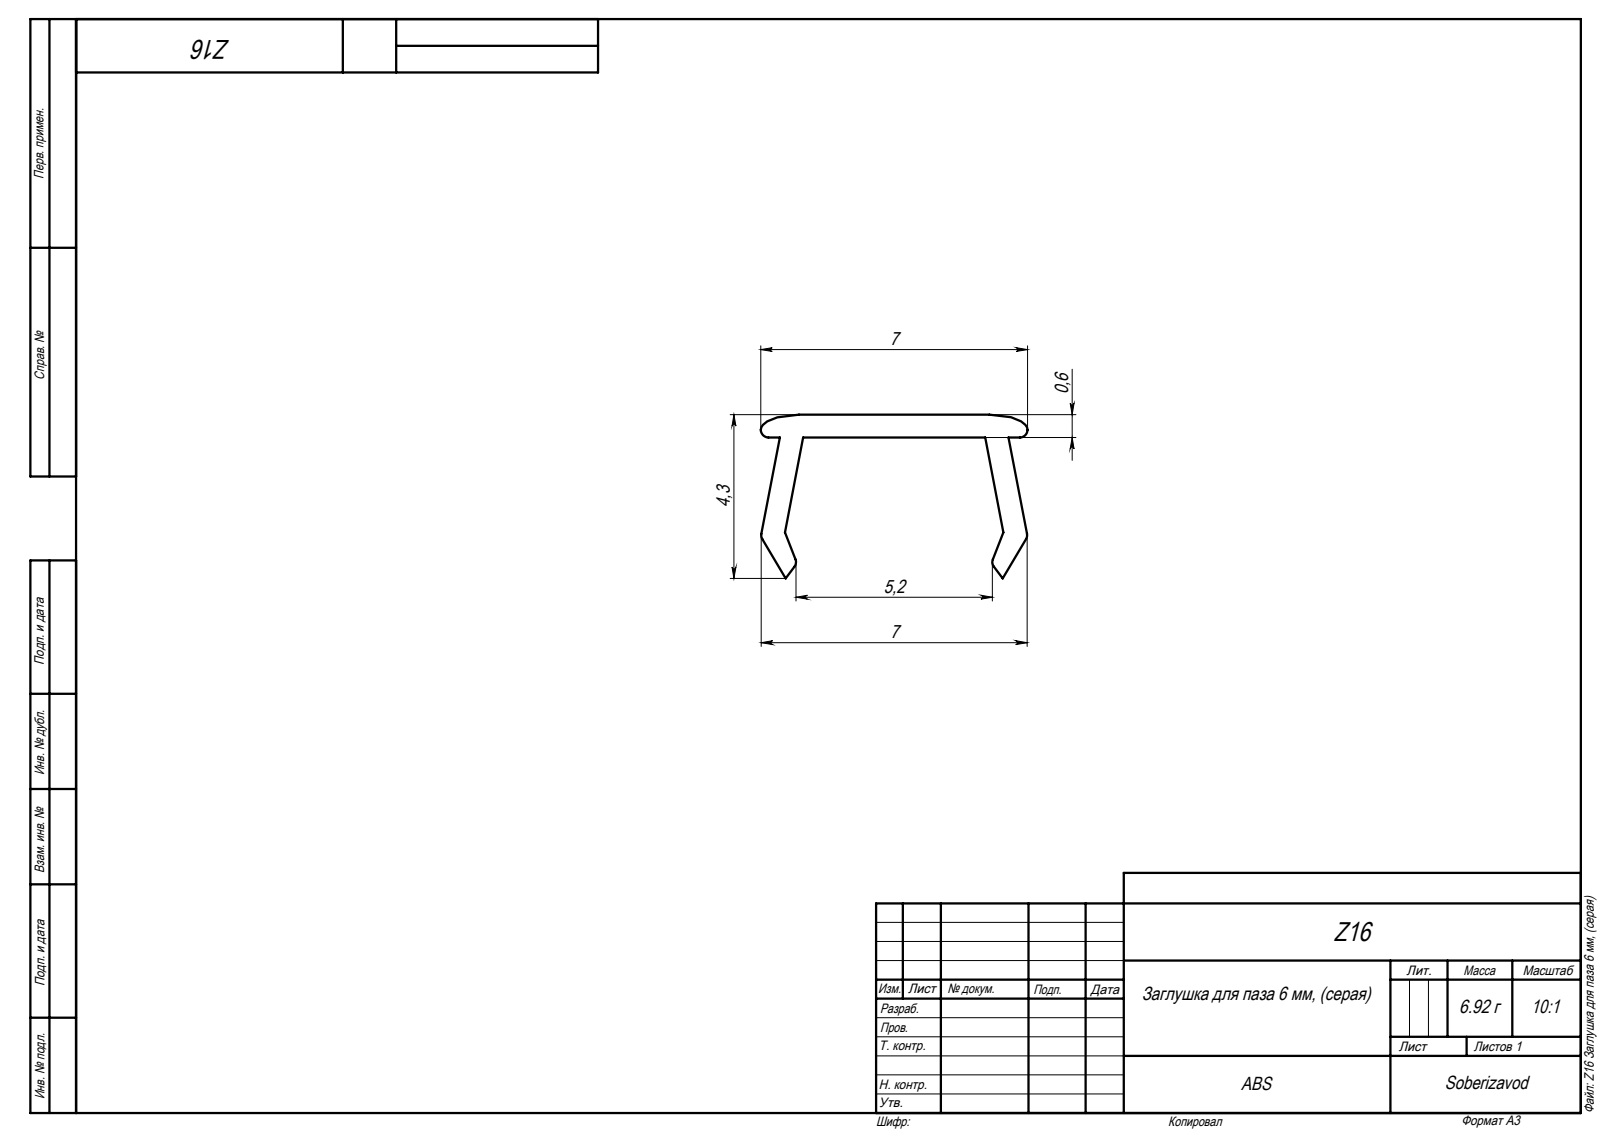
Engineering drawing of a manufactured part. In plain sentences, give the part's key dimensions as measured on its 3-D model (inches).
The part is named "Z16 Заглушка для паза 6 мм, (серая)". Its 3-D file was written by "SolidWorks 2018 (AUTOMOTIVE_DESIGN)". It is 1 solid with 26 faces: 16 planar, 8 cylindrical and 2 other. Overall it measures 39.37 by 0.276 by 0.169 inches. Its volume is 0.504 cubic inches and its surface area 44.85 square inches. Partial cylindrical surfaces (rounded edges, fillets, slot ends): 6 of radius 0.008. The main face-to-face distances are 0.024, 39.37.
